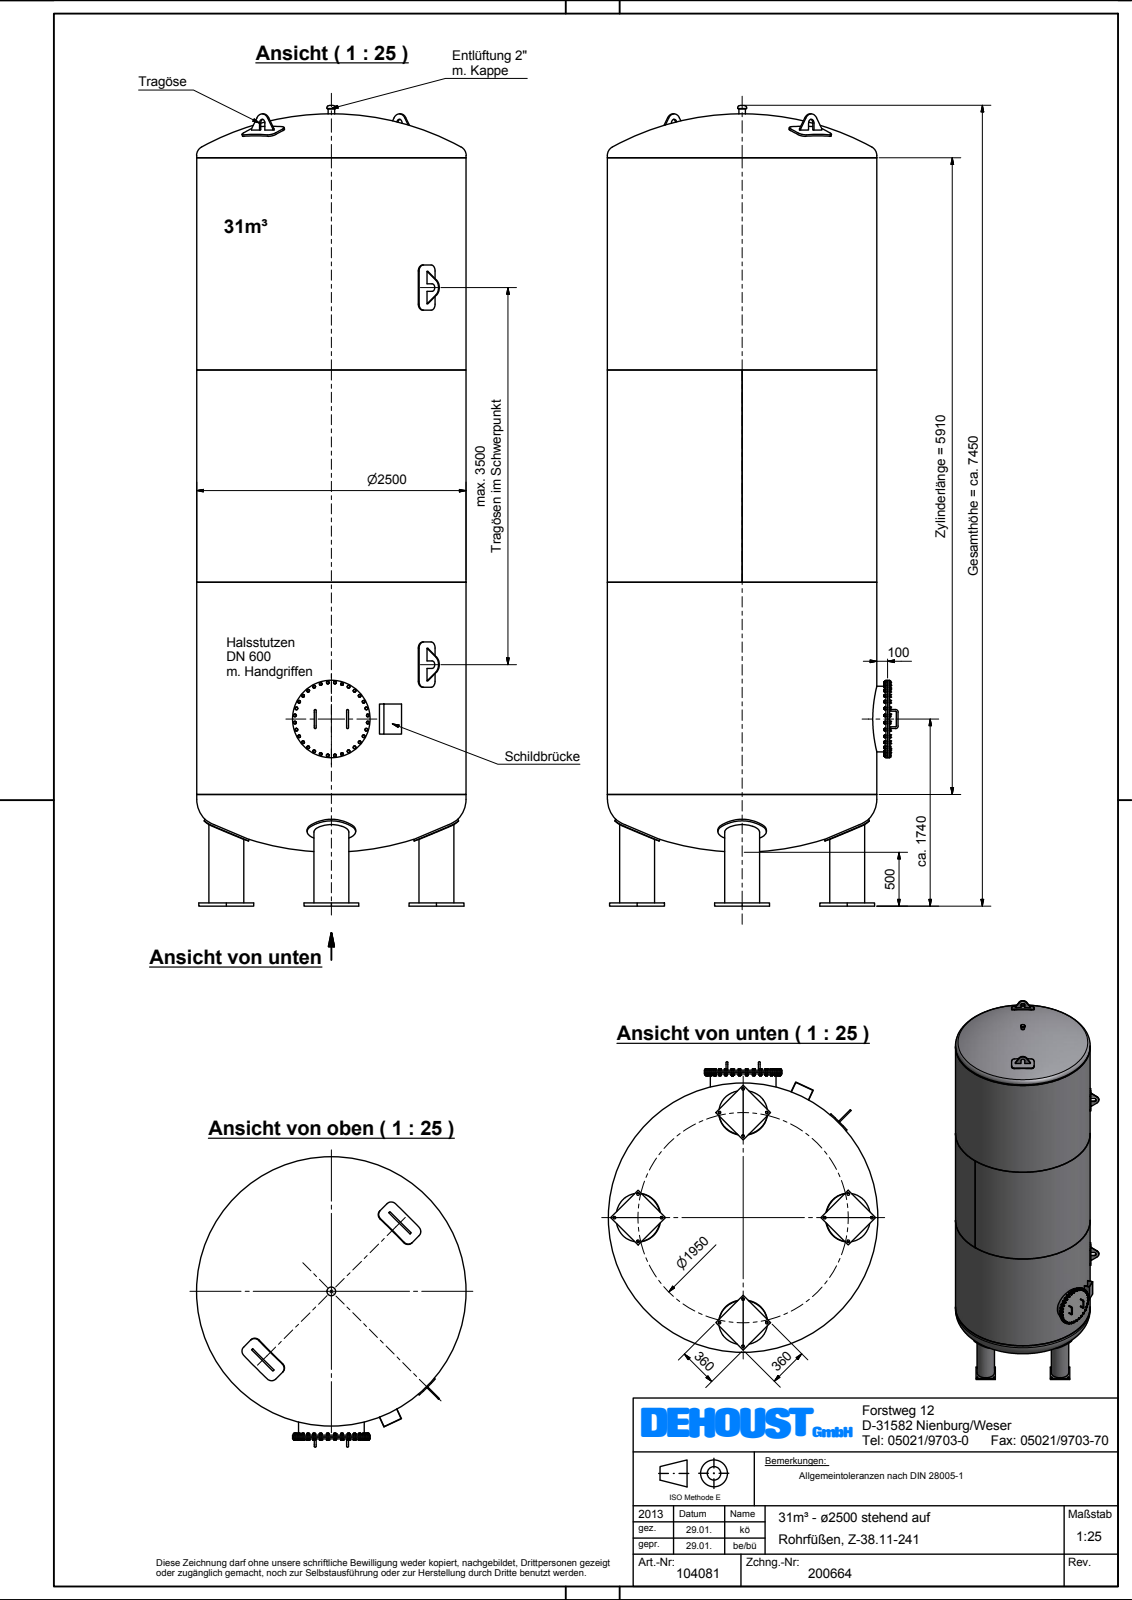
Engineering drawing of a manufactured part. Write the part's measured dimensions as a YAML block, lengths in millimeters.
part_name: "Beh\\S\\dlter_Z-38_11-241_2000_031_KV"
step_written_by: "Autodesk Inventor 2012 (AUTOMOTIVE_DESIGN)"
units: millimeters
bodies: {solids: 6, faces: 192, planar: 107, cylindrical: 55, other: 30}
overall_size: [7353.78, 2619, 2500]
volume: 2220000000
surface_area: 124200000
round_holes:
  - {diameter: 200, count: 4}
  - {diameter: 306.9, count: 4}
  - {diameter: 60.3, count: 1}
  - {diameter: 598, count: 1}
  - {diameter: 2486, count: 1}
  - {diameter: 2488, count: 1}
round_bosses_or_shafts:
  - {diameter: 450, count: 4}
  - {diameter: 323.9, count: 4}
  - {diameter: 2500, count: 1}
  - {diameter: 720, count: 1}
  - {diameter: 610, count: 1}
partial_cylinders:
  - {radius: 56, count: 16}
  - {radius: 35, count: 3}
  - {radius: 85, count: 3}
  - {radius: 1260, count: 1}
face_to_face_distances: [1036.54, 30, 1006.54, 16, 1378.65, 359.95, 2.95, 176.98, 2.91, 10]
hole_center_spacings: [975, 1378.86, 1950]
